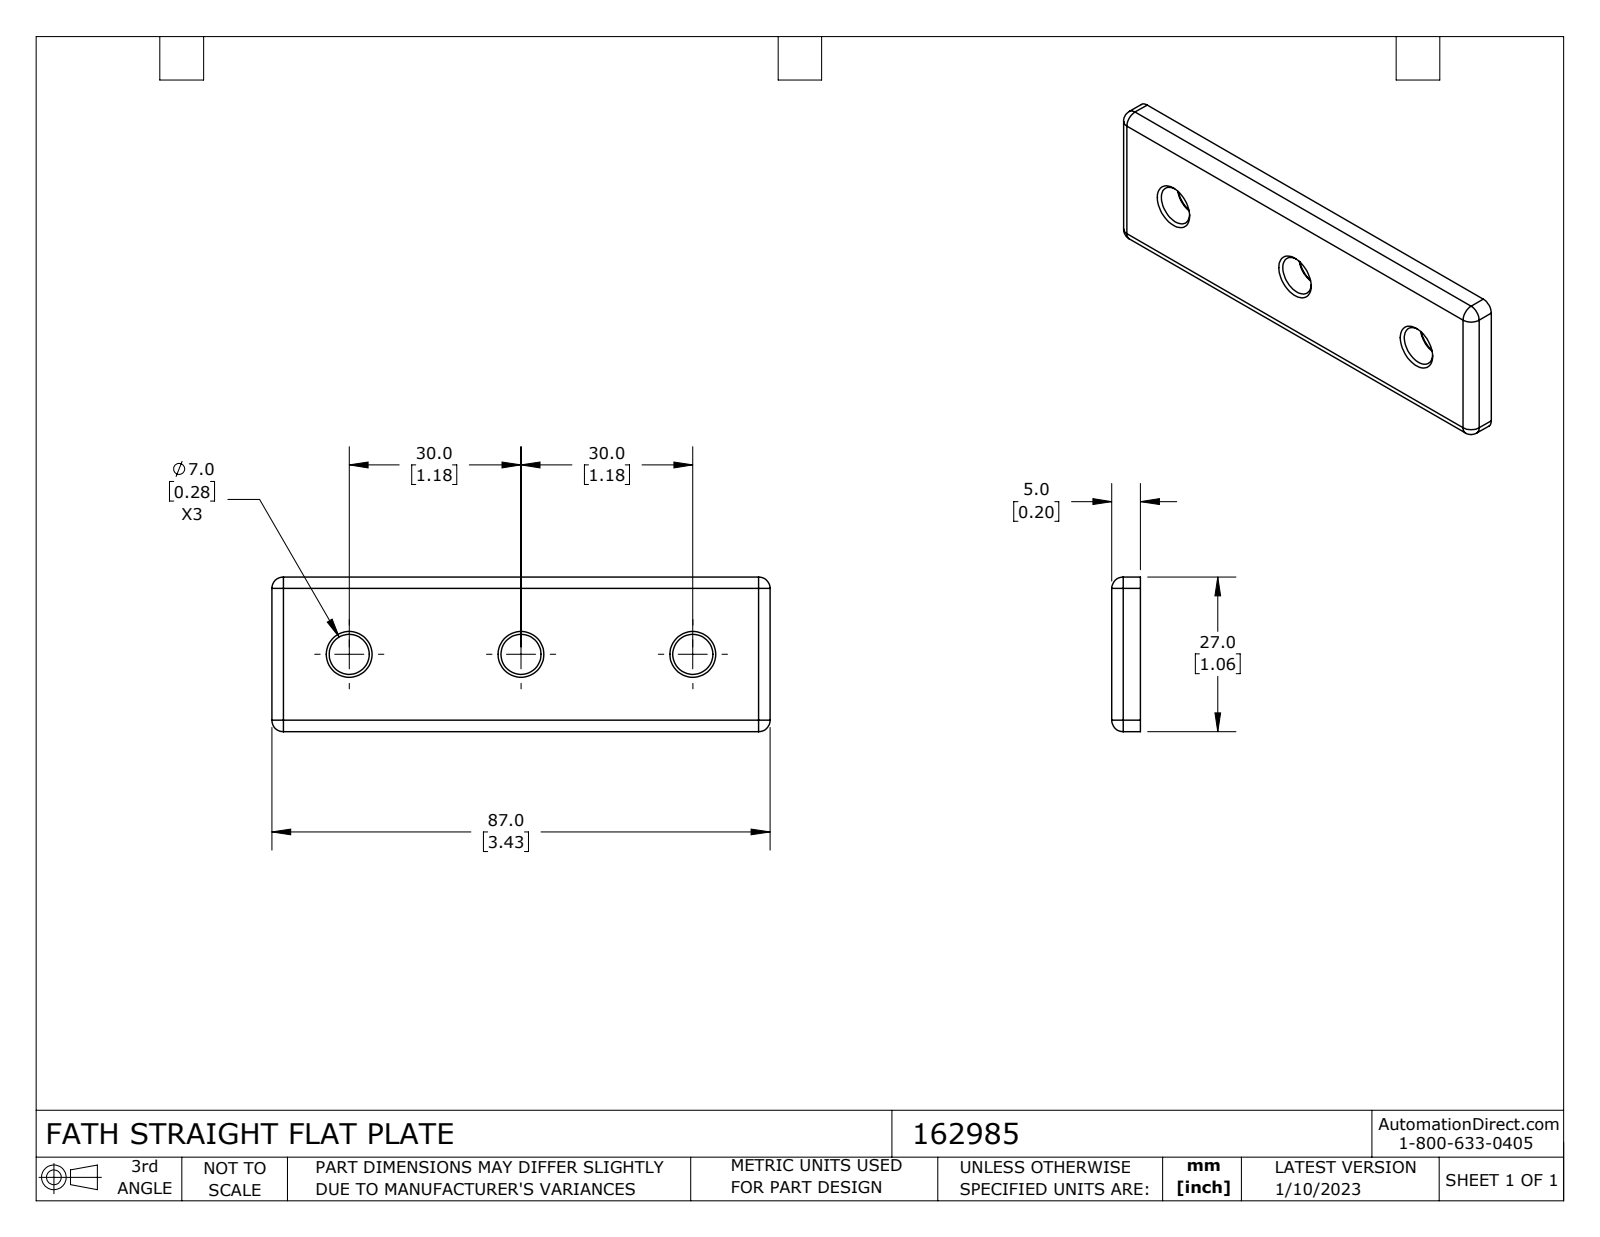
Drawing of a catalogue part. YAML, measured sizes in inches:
part_name: "162985"
step_written_by: "SolidWorks 2021 (CONFIG_CONTROL_DESIGN)"
units: inches
bodies: {solids: 1, faces: 36, planar: 6, cylindrical: 14, other: 16}
overall_size: [3.425, 1.063, 0.197]
volume: 0.668
surface_area: 8.807
round_holes:
  - {diameter: 0.276, count: 3}
partial_cylinders:
  - {radius: 0.079, count: 8}
face_to_face_distances: [0.197, 1.063, 3.425]
hole_center_spacings: [1.181, 2.362]
